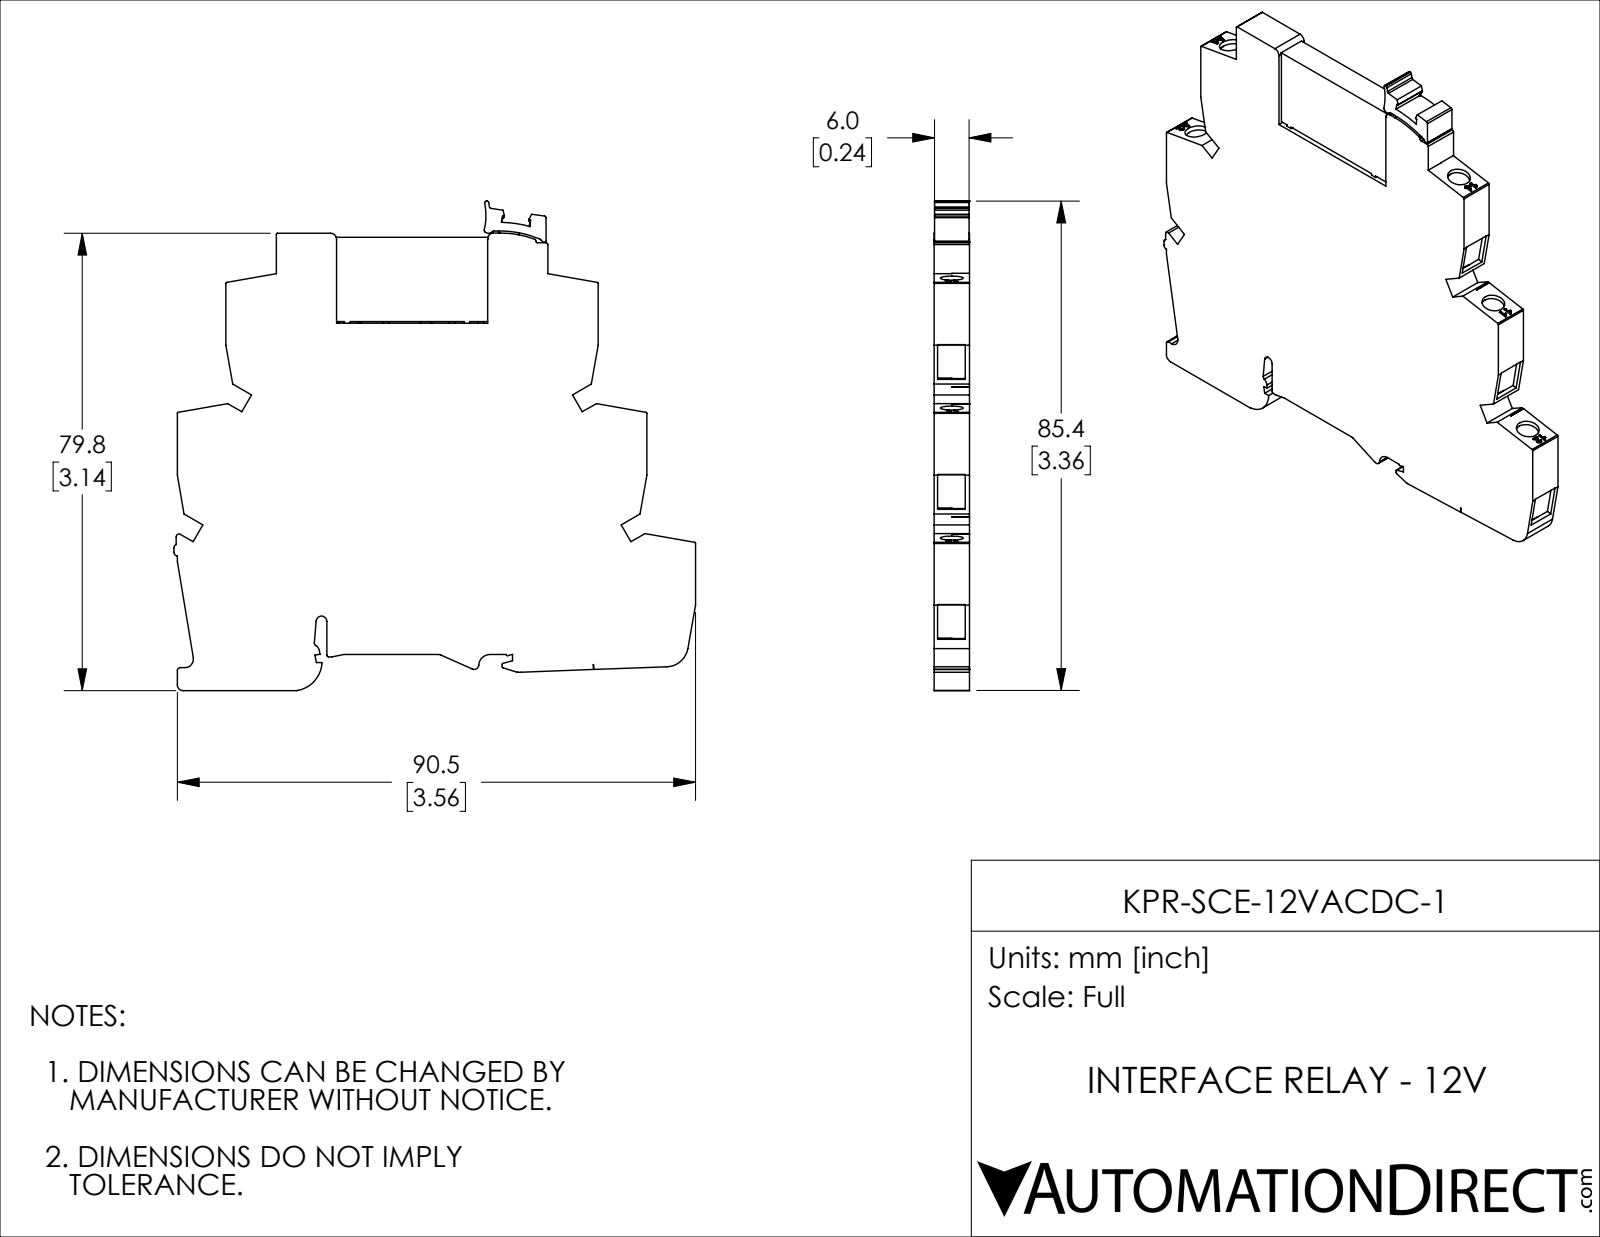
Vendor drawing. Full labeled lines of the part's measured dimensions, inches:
Part name (STEP PRODUCT): KPR-SCE-12VACDC-1
STEP written by: SolidWorks 2018 (AUTOMOTIVE_DESIGN)
Units: inches
Bodies: 1 solid, 422 faces (304 planar, 90 cylindrical, 28 other)
Overall size (bounding box): 3.586 × 3.364 × 0.244
Volume: 2.104 in³ · Surface area: 23.55 in²
Round holes (diameter × count): ⌀0.157 ×5
Round bosses / shafts (diameter × count): ⌀0.016 ×2
Partial cylindrical surfaces — rounded edges, fillets, slot ends (radius × count): R0.008 ×15, R0.012 ×10, R0.039 ×10, R0.02 ×5, R0.037 ×5, R0.079 ×3, R0.004 ×2, R0.024 ×2
Main face-to-face distances: 0.244, 0.024, 0.22, 0.033, 0.197, 0.335, 0.031, 0.821, 3.228, 2.894
Hole centre spacings: 0.485, 0.485, 0.969
